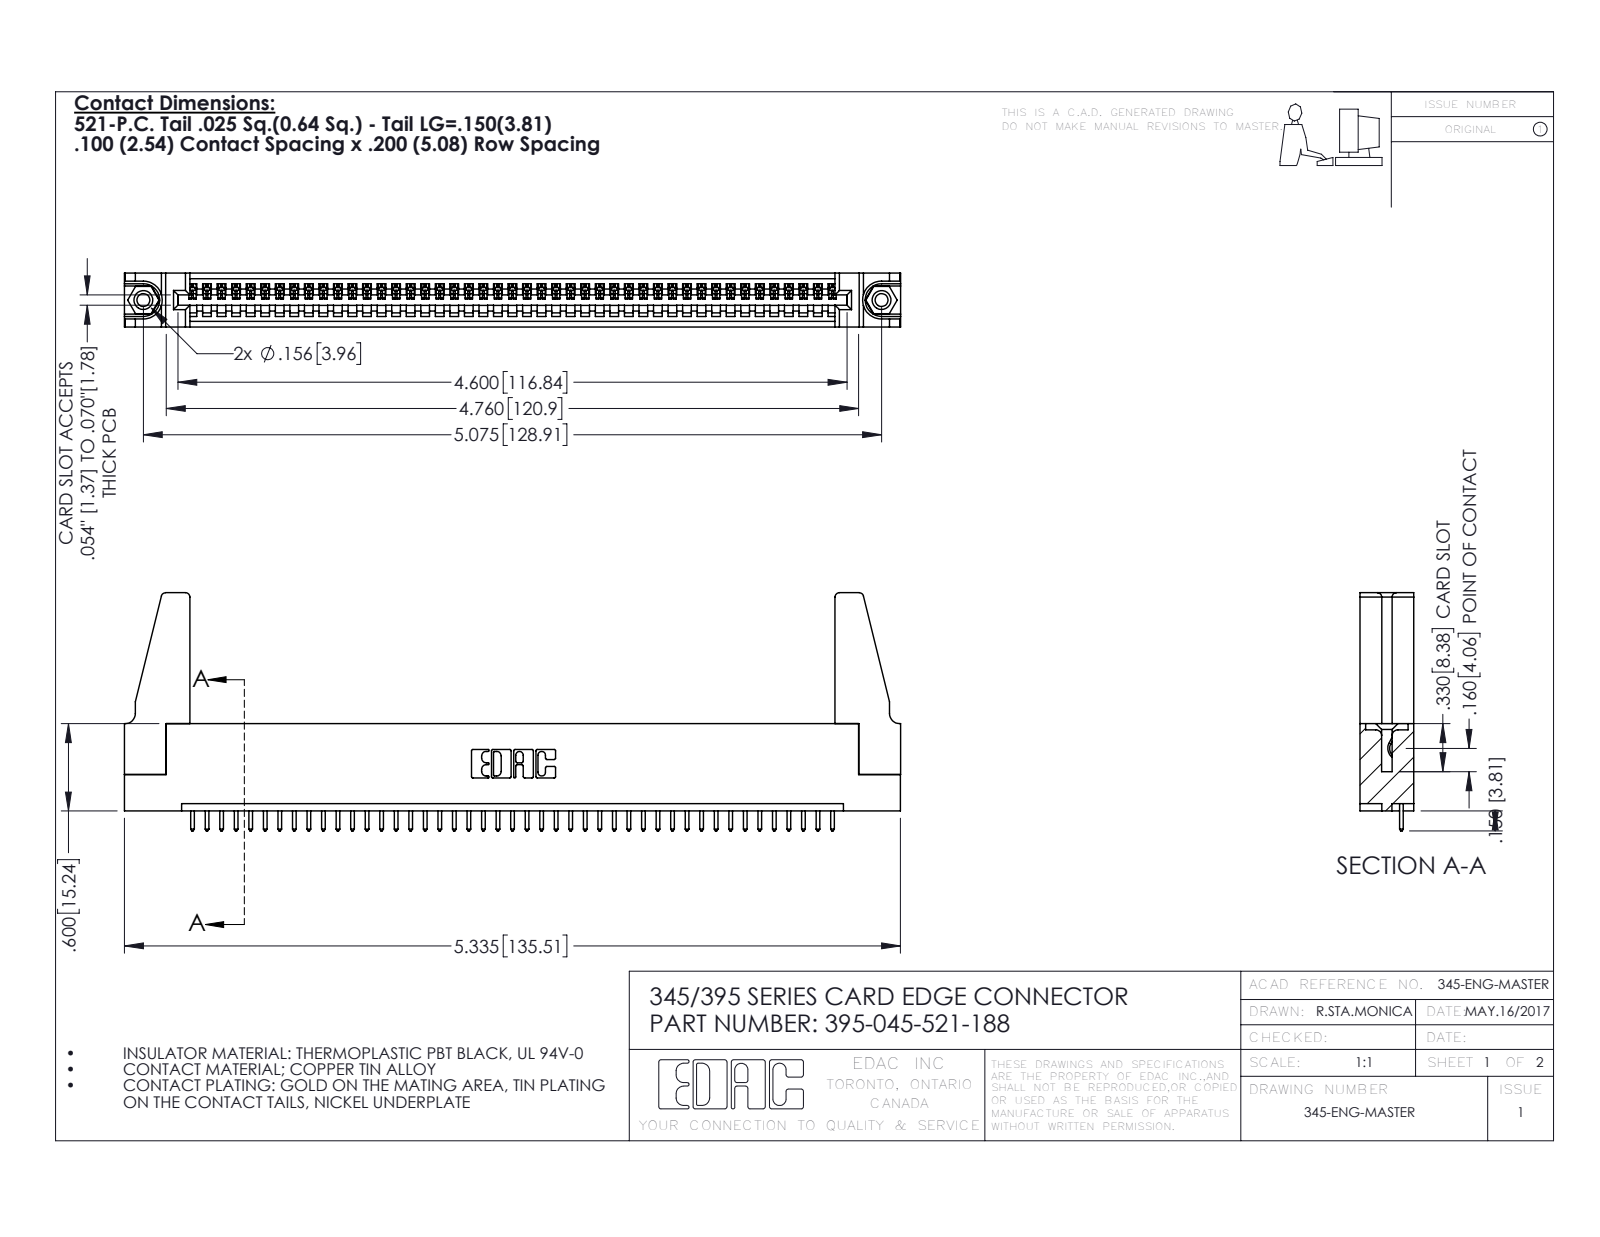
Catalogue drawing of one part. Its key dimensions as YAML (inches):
part_name: "345-250-001_345-250-001-102; 345-292-001_345-293-121; 345 Part_Flush Mounting Lugs - 0.156 Dia-TH; 395-045-521-188 (+1 more)"
step_written_by: "SolidWorks 2016 (CONFIG_CONTROL_DESIGN)"
units: inches
bodies: {solids: 50, faces: 2860, planar: 1952, cylindrical: 892, other: 16}
overall_size: [5.336, 1.637, 0.37]
volume: 0.978
surface_area: 30.44
round_holes:
  - {diameter: 0.089, count: 2}
  - {diameter: 0.125, count: 2}
  - {diameter: 0.156, count: 2}
  - {diameter: 0.064, count: 1}
round_bosses_or_shafts:
  - {diameter: 0.155, count: 2}
partial_cylinders:
  - {radius: 0.006, count: 90}
  - {radius: 0.01, count: 90}
  - {radius: 0.01, count: 22}
  - {radius: 0.03, count: 8}
  - {radius: 0.007, count: 6}
  - {radius: 0.031, count: 6}
  - {radius: 0.026, count: 3}
  - {radius: 0.031, count: 2}
face_to_face_distances: [0.072, 0.298, 0.37, 0.2, 0.098, 0.272, 0.025, 0.225, 0.149, 0.072]
hole_center_spacings: [0.27, 4.839, 5.075]
